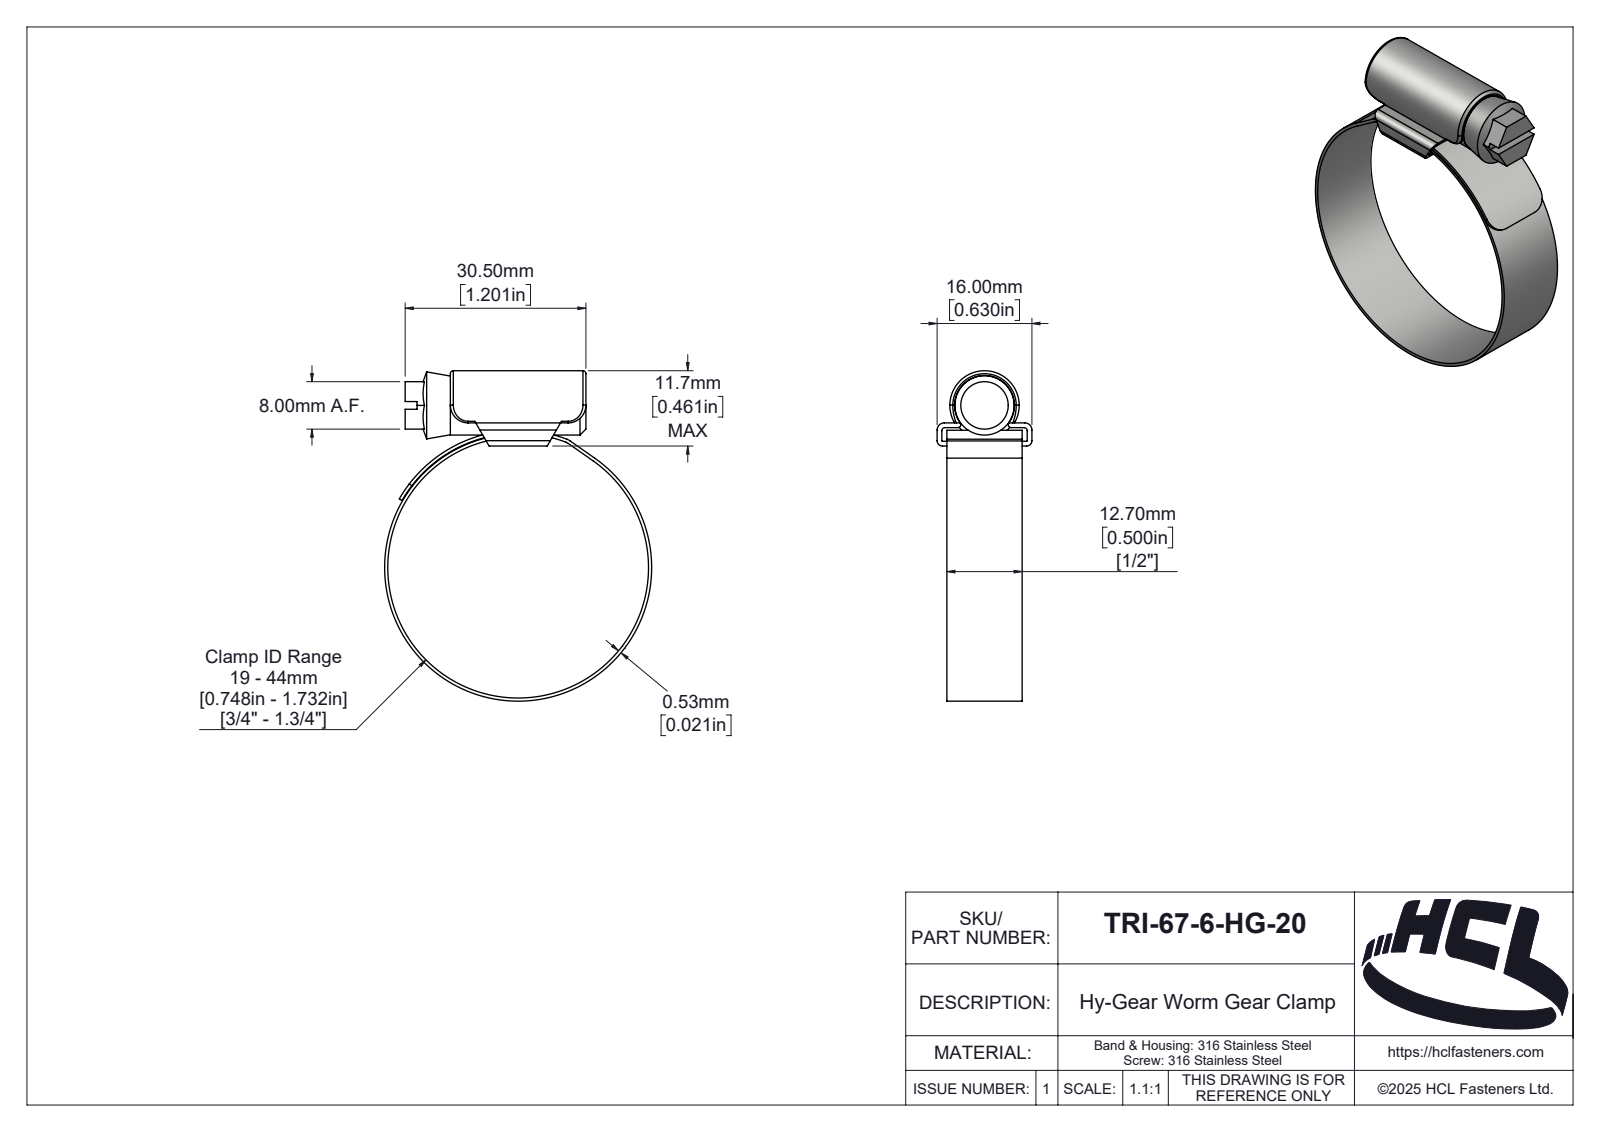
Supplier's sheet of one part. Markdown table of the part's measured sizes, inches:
| quantity | value |
| --- | --- |
| part name | TRI-57-0-HG-20 |
| STEP written by | SolidWorks 2025 (AUTOMOTIVE_DESIGN) |
| units | inches |
| bodies | 3 solids, 189 faces (39 planar, 89 cylindrical, 61 other) |
| overall size | 2.194 × 1.774 × 0.63 |
| volume | 0.25 in³ |
| surface area | 11.23 in² |
| round holes (diameter × count) | 1.732 × 1 |
| round bosses / shafts (diameter × count) | 1.774 × 1, 0.394 × 1 |
| partial cylindrical surfaces (radius × count) | 0.02 × 6, 0.118 × 4, 0.004 × 2, 0.035 × 2, 0.047 × 2, 0.018 × 1, 0.074 × 1, 0.079 × 1 |
| main face-to-face distances | 0.031, 0.122, 0.5, 0.091, 0.021, 0.154, 1.201, 0.065, 0.565, 0.598 |
